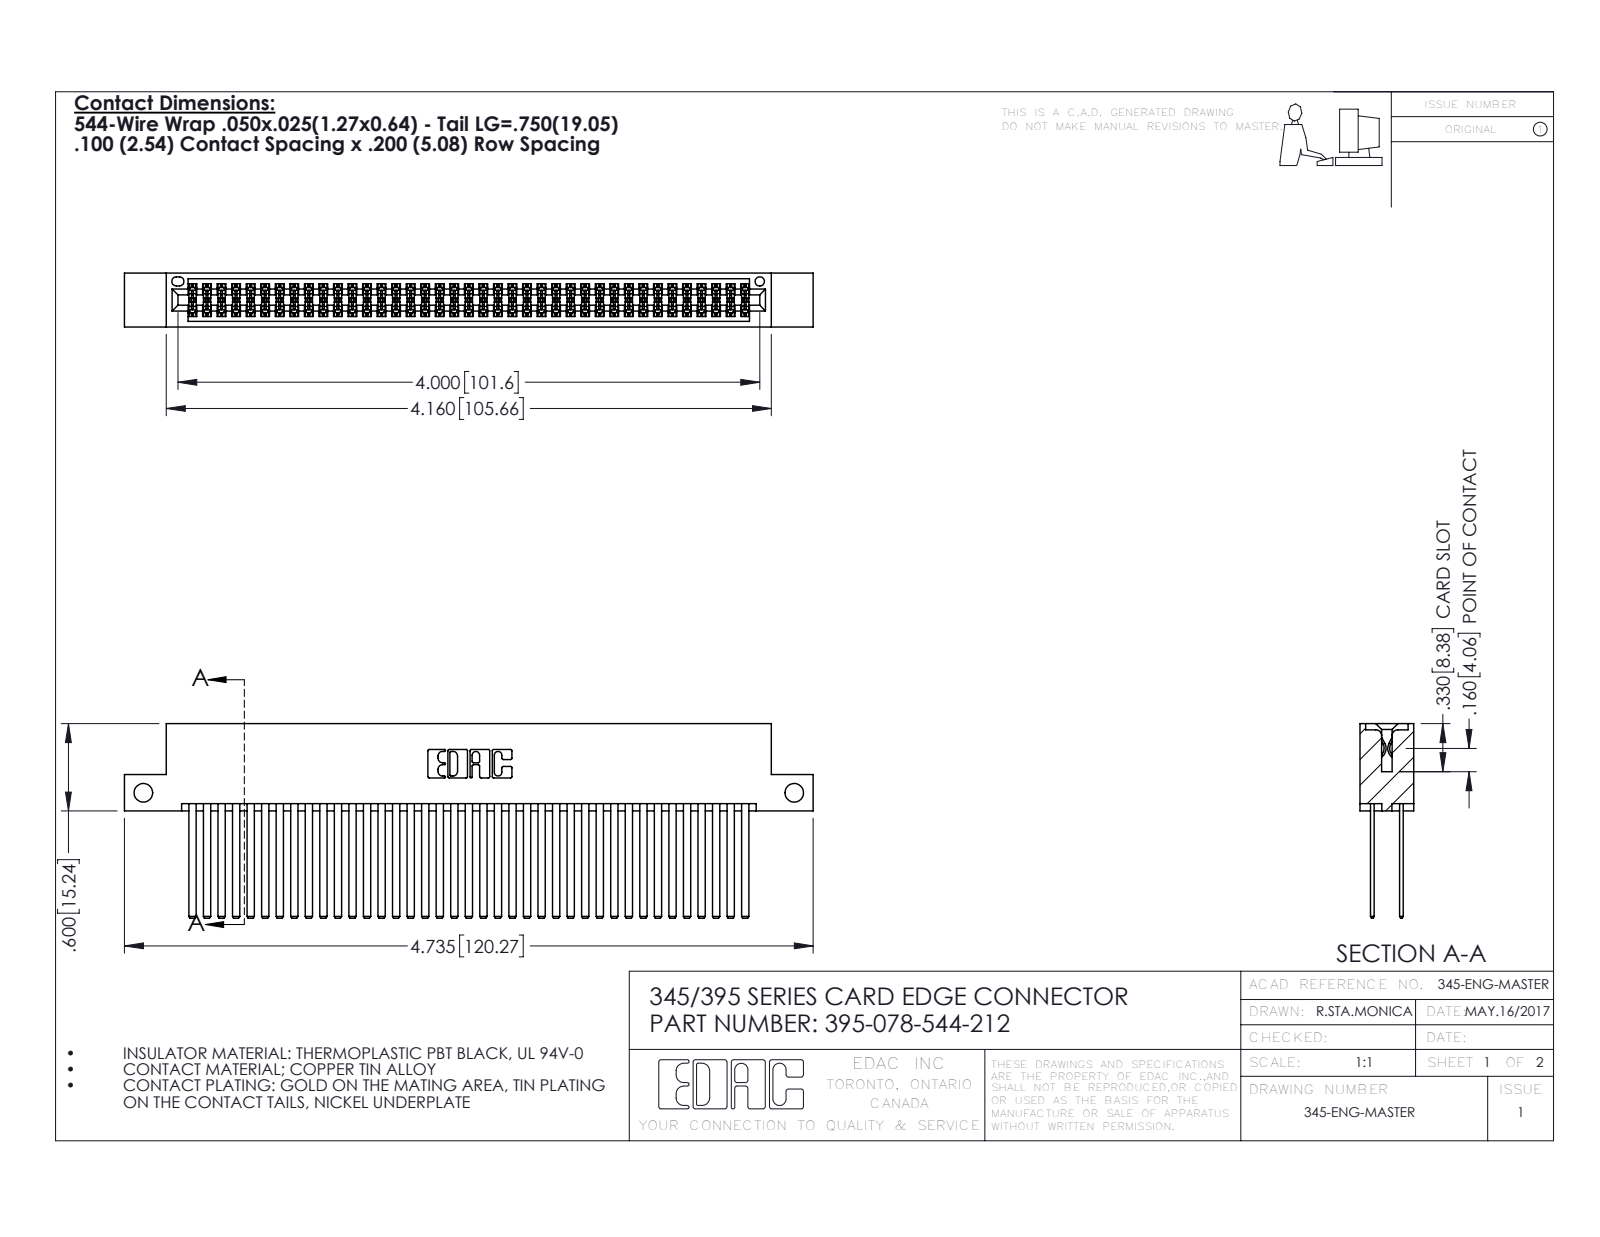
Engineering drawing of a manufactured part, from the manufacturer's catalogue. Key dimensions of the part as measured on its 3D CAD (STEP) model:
Part name (STEP PRODUCT): 345-292-001_345-293-144; 395-078-544-212; 345 Part_Flush Mounting Lugs - Side Mount
STEP written by: SolidWorks 2016 (CONFIG_CONTROL_DESIGN)
Units: inches
Bodies: 79 solids, 3558 faces (2342 planar, 1216 cylindrical, 0 other)
Overall size (bounding box): 4.735 × 1.337 × 0.37
Volume: 0.773 in³ · Surface area: 33.68 in²
Round holes (diameter × count): ⌀0.128 ×2, ⌀0.064 ×1
Partial cylindrical surfaces — rounded edges, fillets, slot ends (radius × count): R0.006 ×117, R0.01 ×22, R0.007 ×6, R0.031 ×6, R0.026 ×3, R0.014 ×2, R0.019 ×2, R0.022 ×2
Main face-to-face distances: 0.2, 0.025, 0.298, 0.072, 0.098, 0.272, 0.225, 0.175, 0.37, 0.05
Hole centre spacings: 4.475
